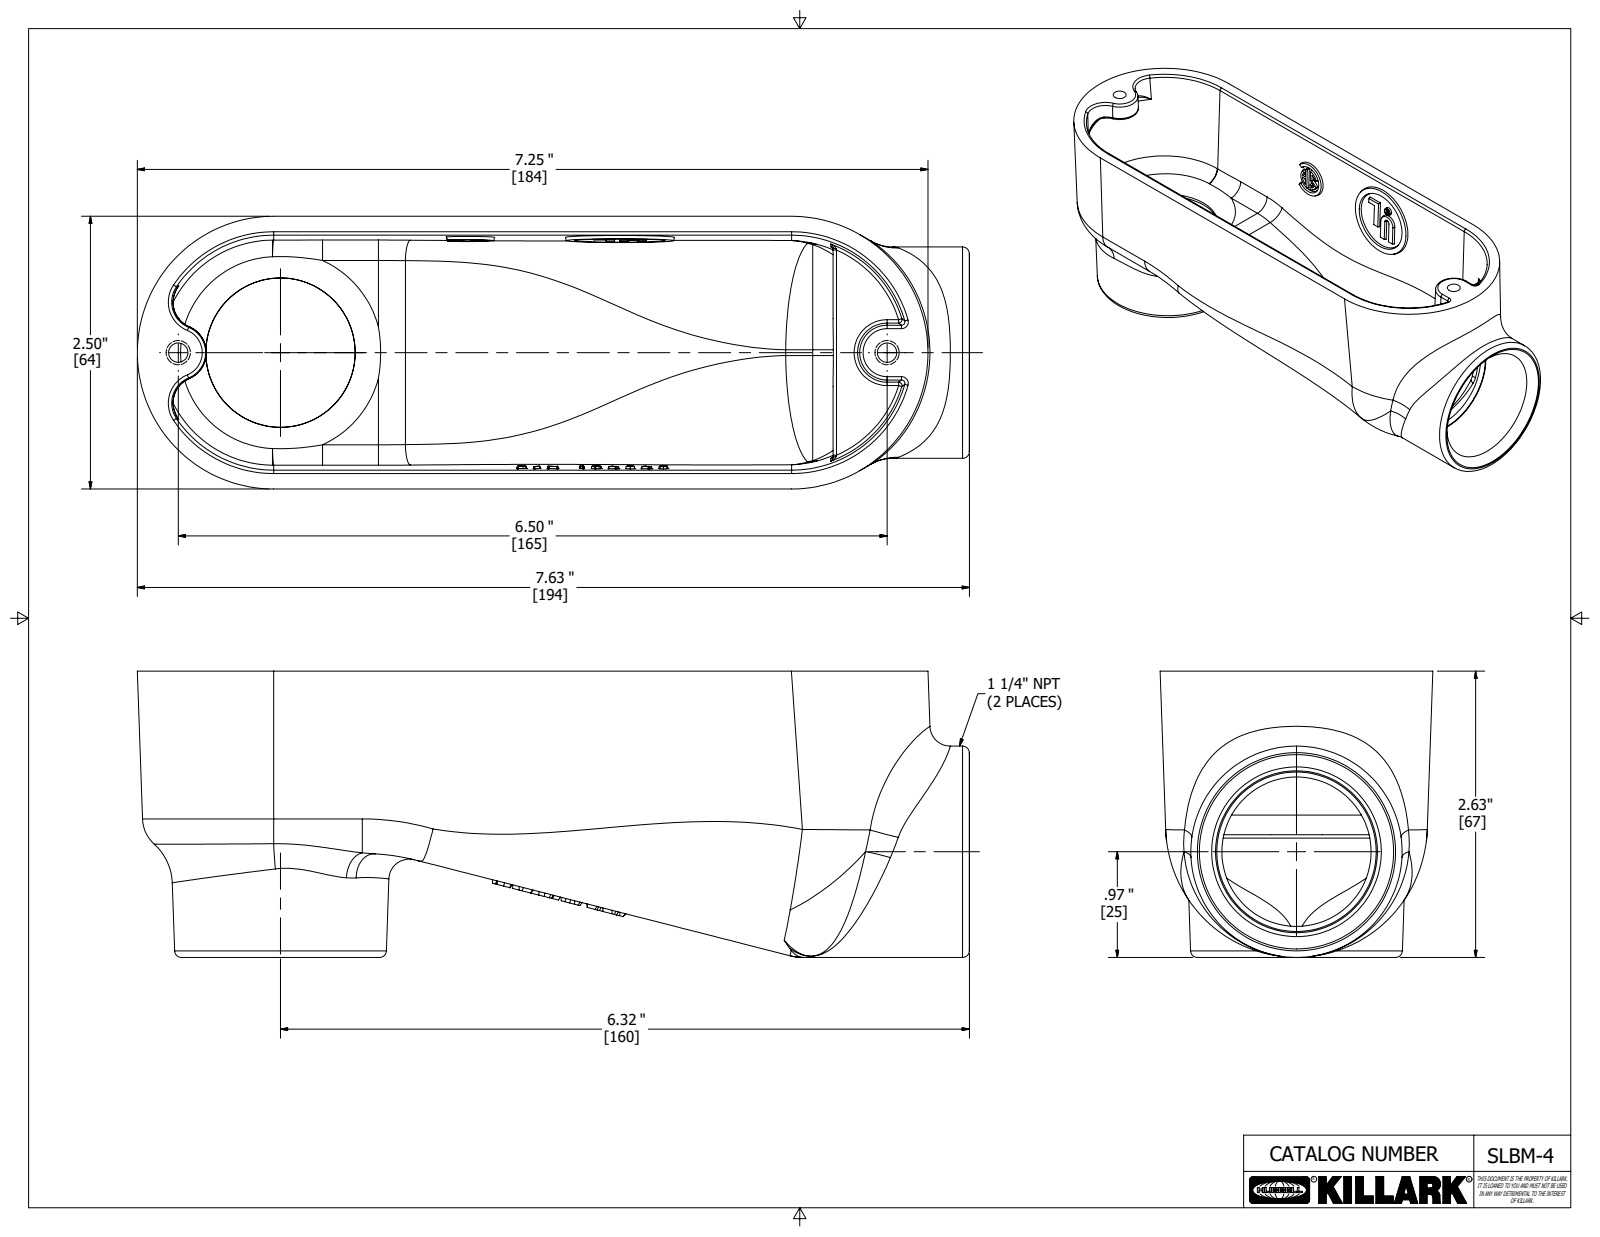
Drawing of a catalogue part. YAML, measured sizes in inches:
part_name: "0194840 -2"
step_written_by: "Autodesk Inventor 2020 (AUTOMOTIVE_DESIGN)"
units: inches
bodies: {solids: 1, faces: 557, planar: 269, cylindrical: 22, other: 266}
overall_size: [7.63, 2.625, 2.5]
volume: 9.537
surface_area: 104.2
round_holes:
  - {diameter: 0.177, count: 2}
  - {diameter: 1.368, count: 1}
round_bosses_or_shafts:
  - {diameter: 1.937, count: 1}
partial_cylinders:
  - {radius: 0.031, count: 8}
  - {radius: 0.328, count: 2}
  - {radius: 0.5, count: 2}
  - {radius: 1, count: 2}
  - {radius: 0.187, count: 1}
  - {radius: 2, count: 1}
face_to_face_distances: [0.172, 0.174, 0.625, 0.202, 0.03, 1.5, 0.875, 0.25, 1.499, 1.327]
hole_center_spacings: [6.5]
